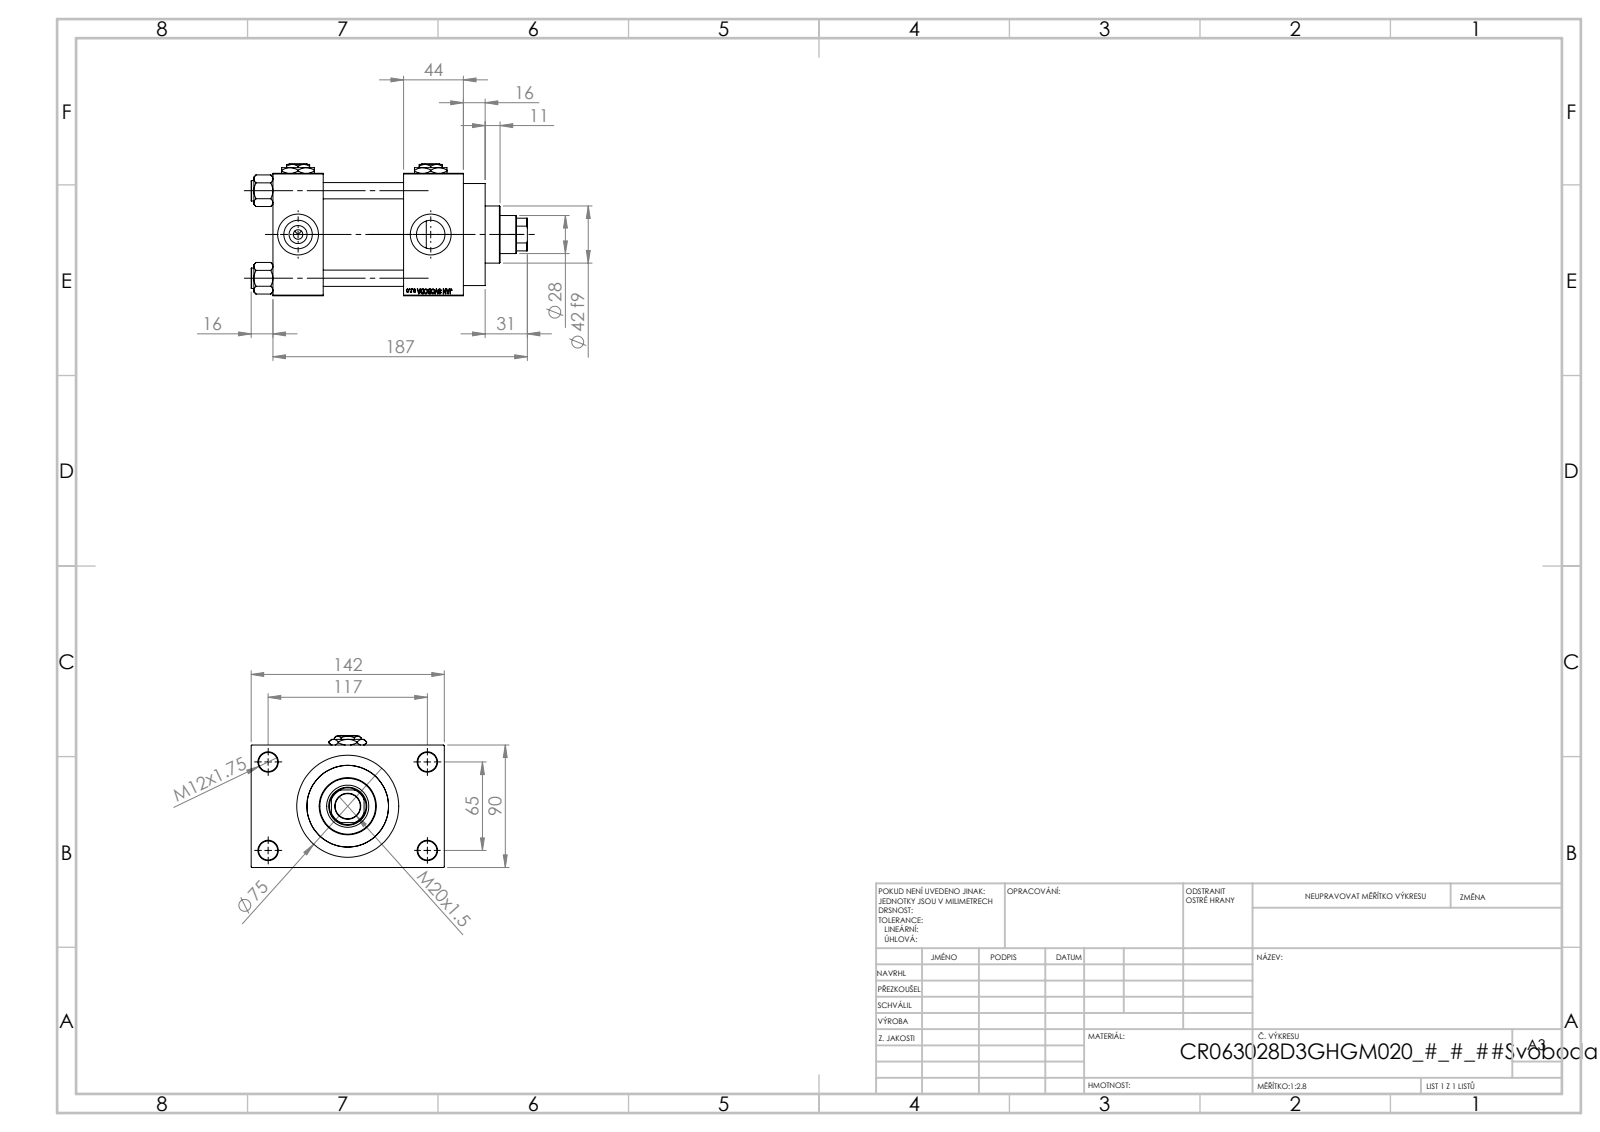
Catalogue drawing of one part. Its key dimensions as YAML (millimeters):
part_name: "NUT_M5_D; V215CR_VCP_D; V215CR_D_Body; V215CR_D_TYCINKA (+2 more)"
step_written_by: "SolidWorks 2019 (CONFIG_CONTROL_DESIGN)"
units: millimeters
bodies: {solids: 13, faces: 1204, planar: 545, cylindrical: 99, other: 560}
overall_size: [203, 142, 97]
volume: 1091000
surface_area: 204942
round_holes:
  - {diameter: 12, count: 4}
  - {diameter: 14, count: 4}
  - {diameter: 20.96, count: 4}
  - {diameter: 30, count: 4}
  - {diameter: 7, count: 3}
  - {diameter: 18.5, count: 1}
  - {diameter: 28, count: 1}
  - {diameter: 31, count: 1}
  - {diameter: 50, count: 1}
  - {diameter: 60, count: 1}
  - {diameter: 63, count: 1}
round_bosses_or_shafts:
  - {diameter: 15, count: 4}
  - {diameter: 75, count: 1}
  - {diameter: 69, count: 1}
  - {diameter: 42, count: 1}
partial_cylinders:
  - {radius: 13.5, count: 1}
face_to_face_distances: [90, 59, 37, 96, 140, 103, 44, 26, 116, 16]
hole_center_spacings: [26.35, 45.47, 64.3, 66.92, 69.81, 90.65, 111.34, 65]
